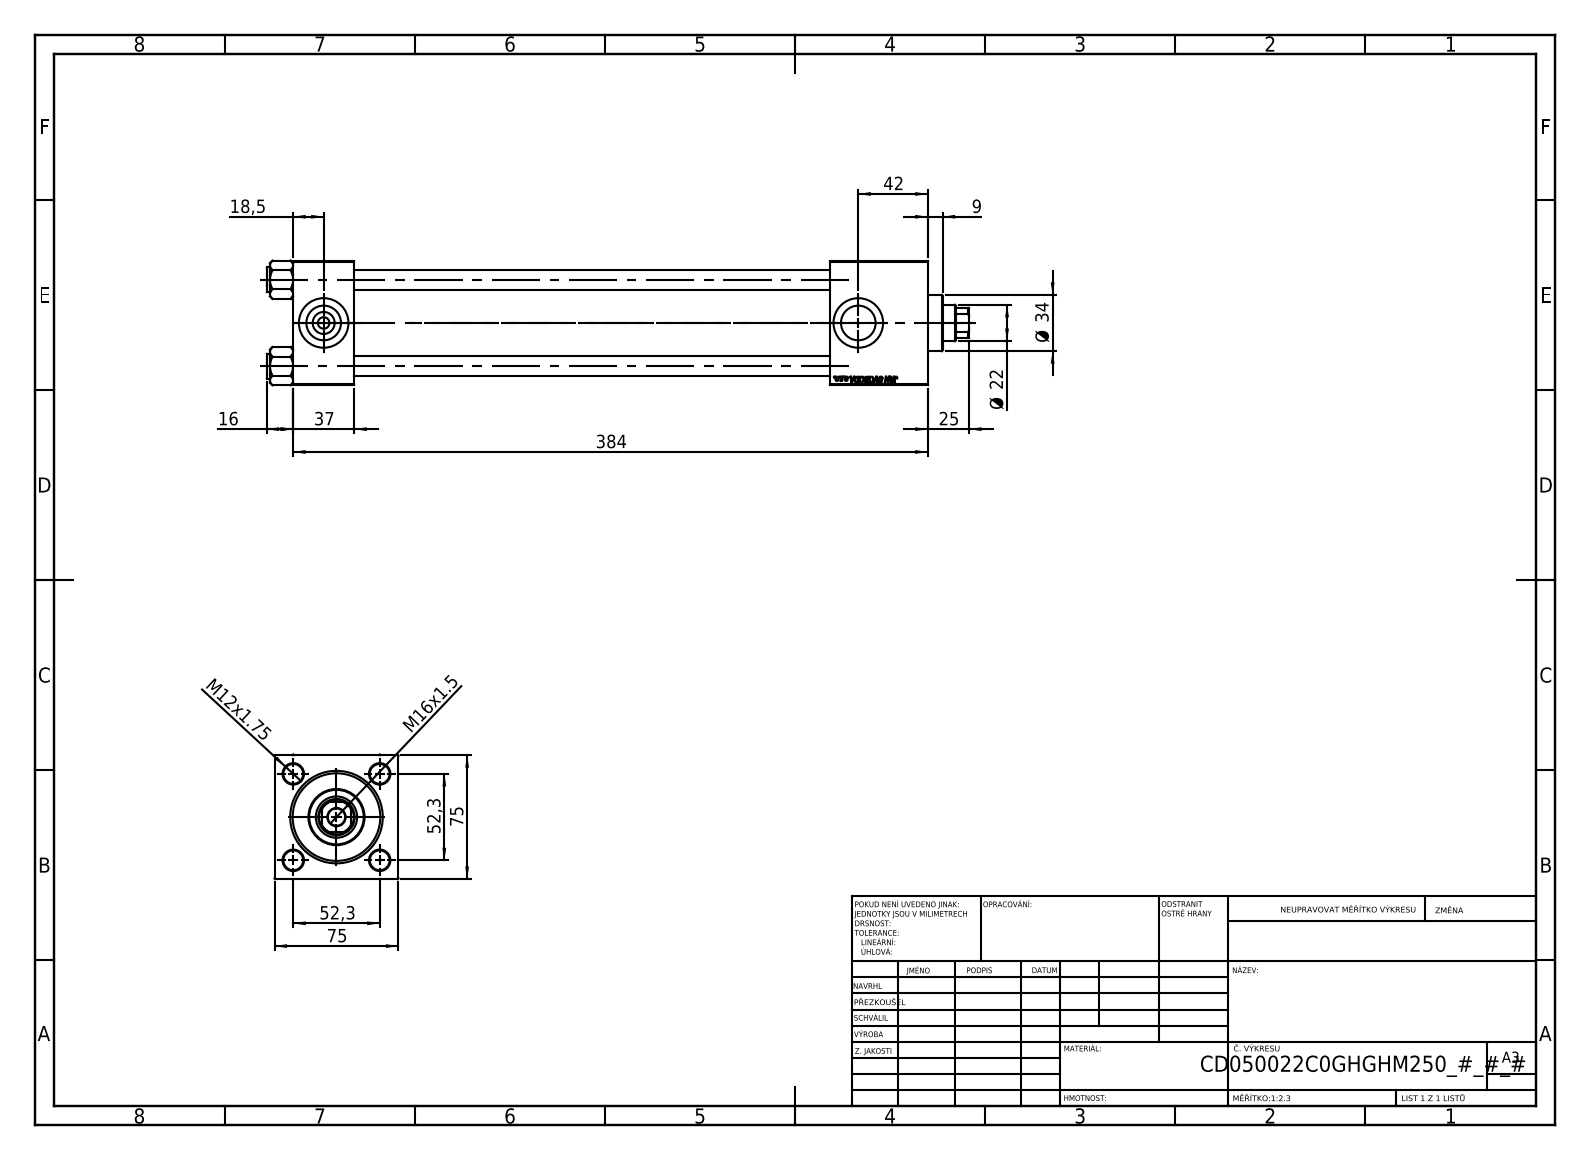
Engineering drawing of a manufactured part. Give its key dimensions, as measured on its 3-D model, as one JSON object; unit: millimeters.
{"part_name": "NUT_M5_V215CD_C; V215CD_Body_C; V215CD_VCP_C; V215CD_VC_C (+1 more)", "step_written_by": "SolidWorks 2019 (CONFIG_CONTROL_DESIGN)", "units": "millimeters", "bodies": {"solids": 11, "faces": 1148, "planar": 526, "cylindrical": 86, "other": 536}, "overall_size": [425, 75.54, 75], "volume_mm3": 963332, "surface_area_mm2": 274457, "round_holes": [[12, 4], [7, 2], [20.96, 2], [30, 2], [10.5, 1], [22, 1], [25, 1], [41, 1], [50, 1], [53, 1]], "round_bosses_or_shafts": [[15, 4], [56, 1], [34, 1]], "partial_cylinders_radius": [[10.5, 1]], "face_to_face_distances": [75, 37, 384, 347, 325, 288, 59, 355.3, 318.3, 30.3], "hole_center_spacings": [36.98, 52.3, 73.96, 323.5]}
